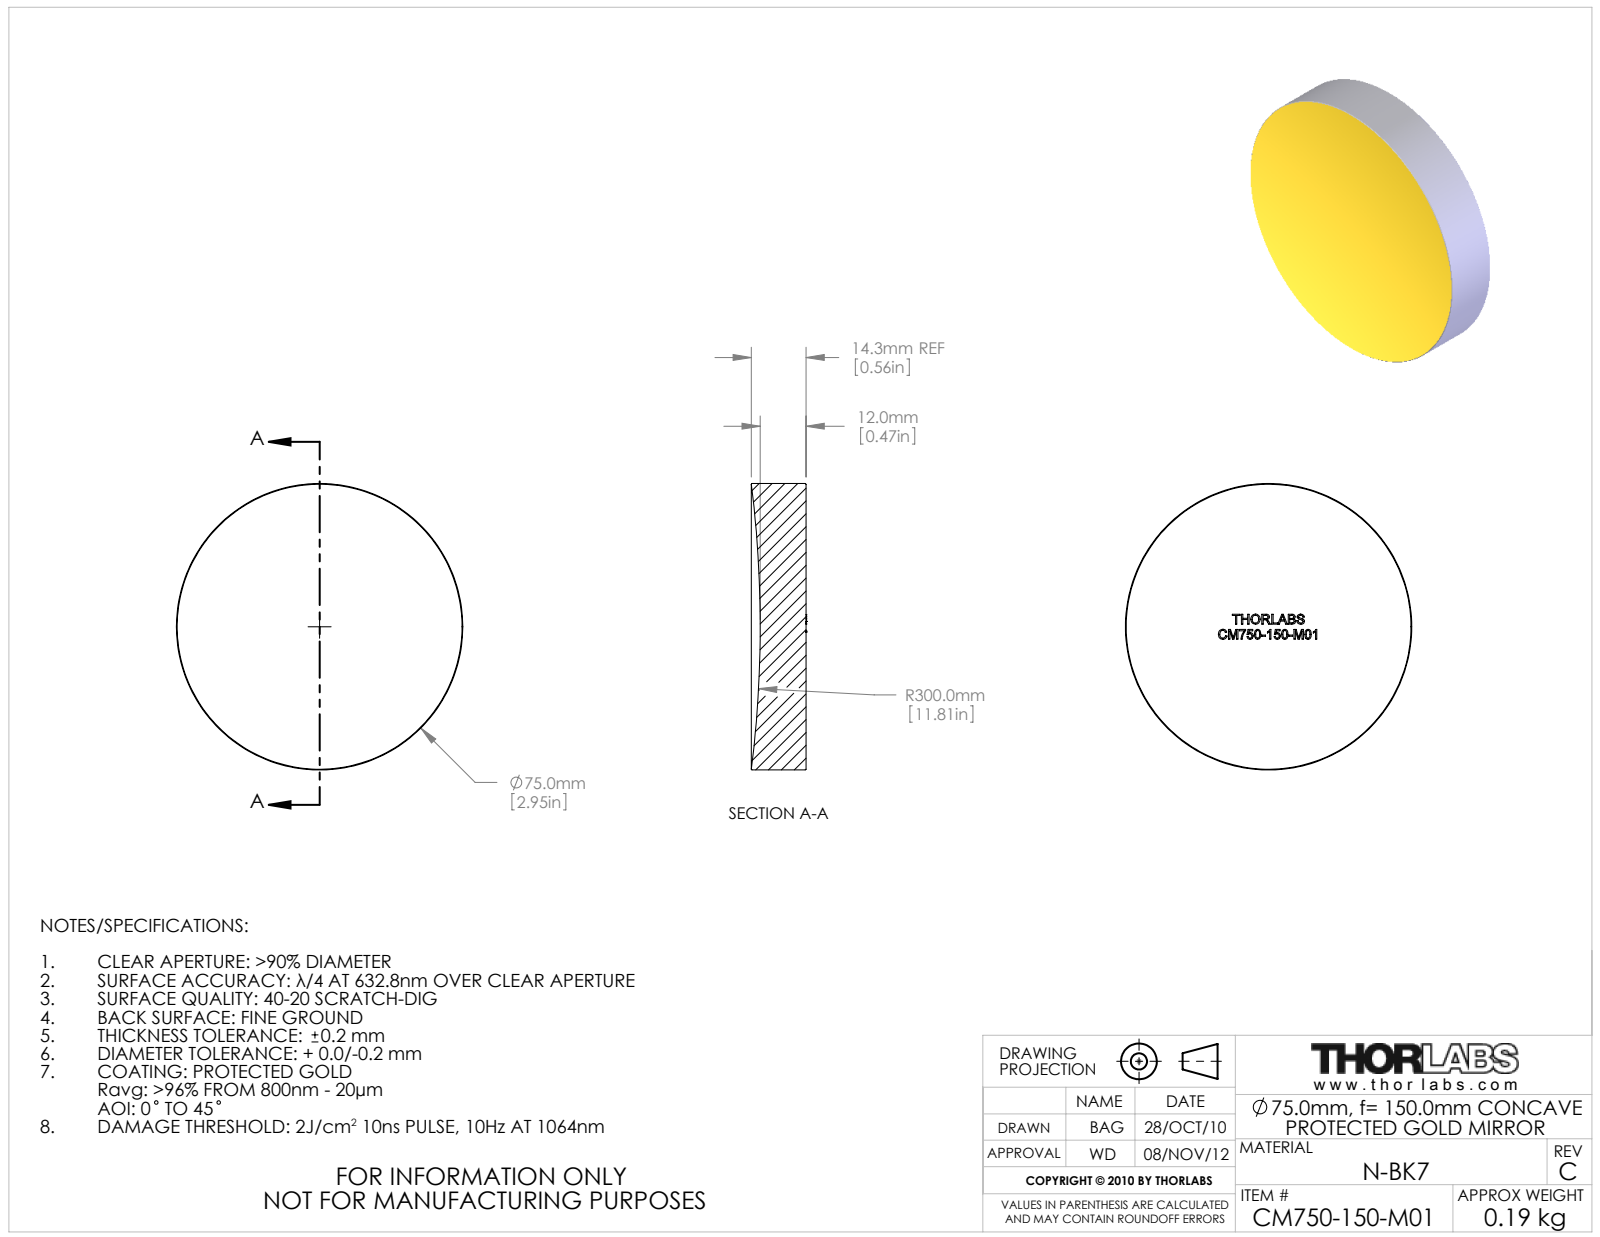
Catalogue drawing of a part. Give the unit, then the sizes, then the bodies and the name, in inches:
Units: inches
Overall size (bounding box): 2.953 × 2.953 × 0.564
Round bosses / shafts (diameter × count): ⌀2.953 ×1
Main face-to-face distances: 0.014, 0.101, 0.015, 0.675, 0.083, 0.097, 0.156, 0.069, 0.089, 0.157
Volume: 3.551 in³ · Surface area: 18.87 in²
Bodies: 1 solid, 271 faces (154 planar, 2 cylindrical, 115 other)
Part name (STEP PRODUCT): 17591-E0W
STEP written by: SolidWorks 2009 (AUTOMOTIVE_DESIGN)
